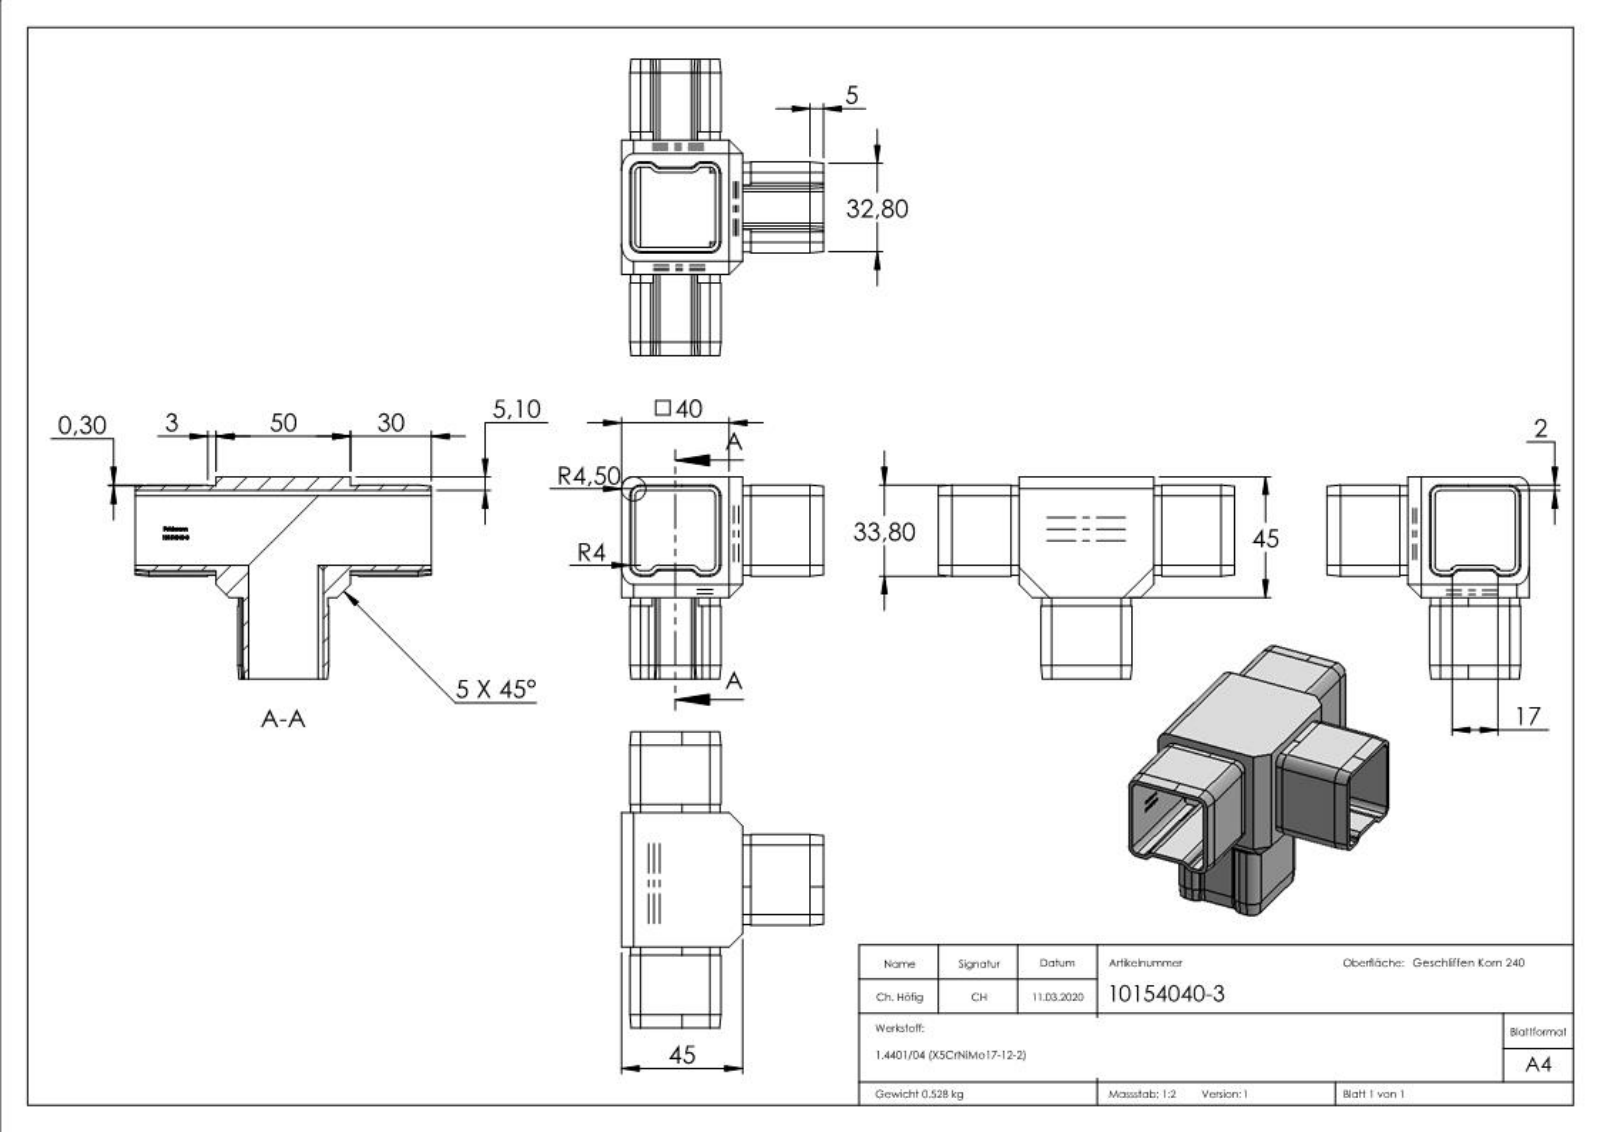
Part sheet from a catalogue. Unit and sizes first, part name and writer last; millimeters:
Units: millimetres
Overall size (bounding box): 110 × 75 × 75
Partial cylindrical surfaces — rounded edges, fillets, slot ends (radius × count): R1.5 ×16, R2 ×12, R3.7 ×12, R4 ×12, R3.5 ×8, R4.5 ×3
Main face-to-face distances: 2, 31.8, 33.8, 4.1, 35.9, 2.1, 35.8, 37.9, 29.8, 42.9
Volume: 61 130 mm³ · Surface area: 46 442 mm²
Bodies: 1 solid, 520 faces (309 planar, 82 cylindrical, 129 other)
Part name (STEP PRODUCT): 10154040-3
STEP written by: SolidWorks 2015 (CONFIG_CONTROL_DESIGN)
